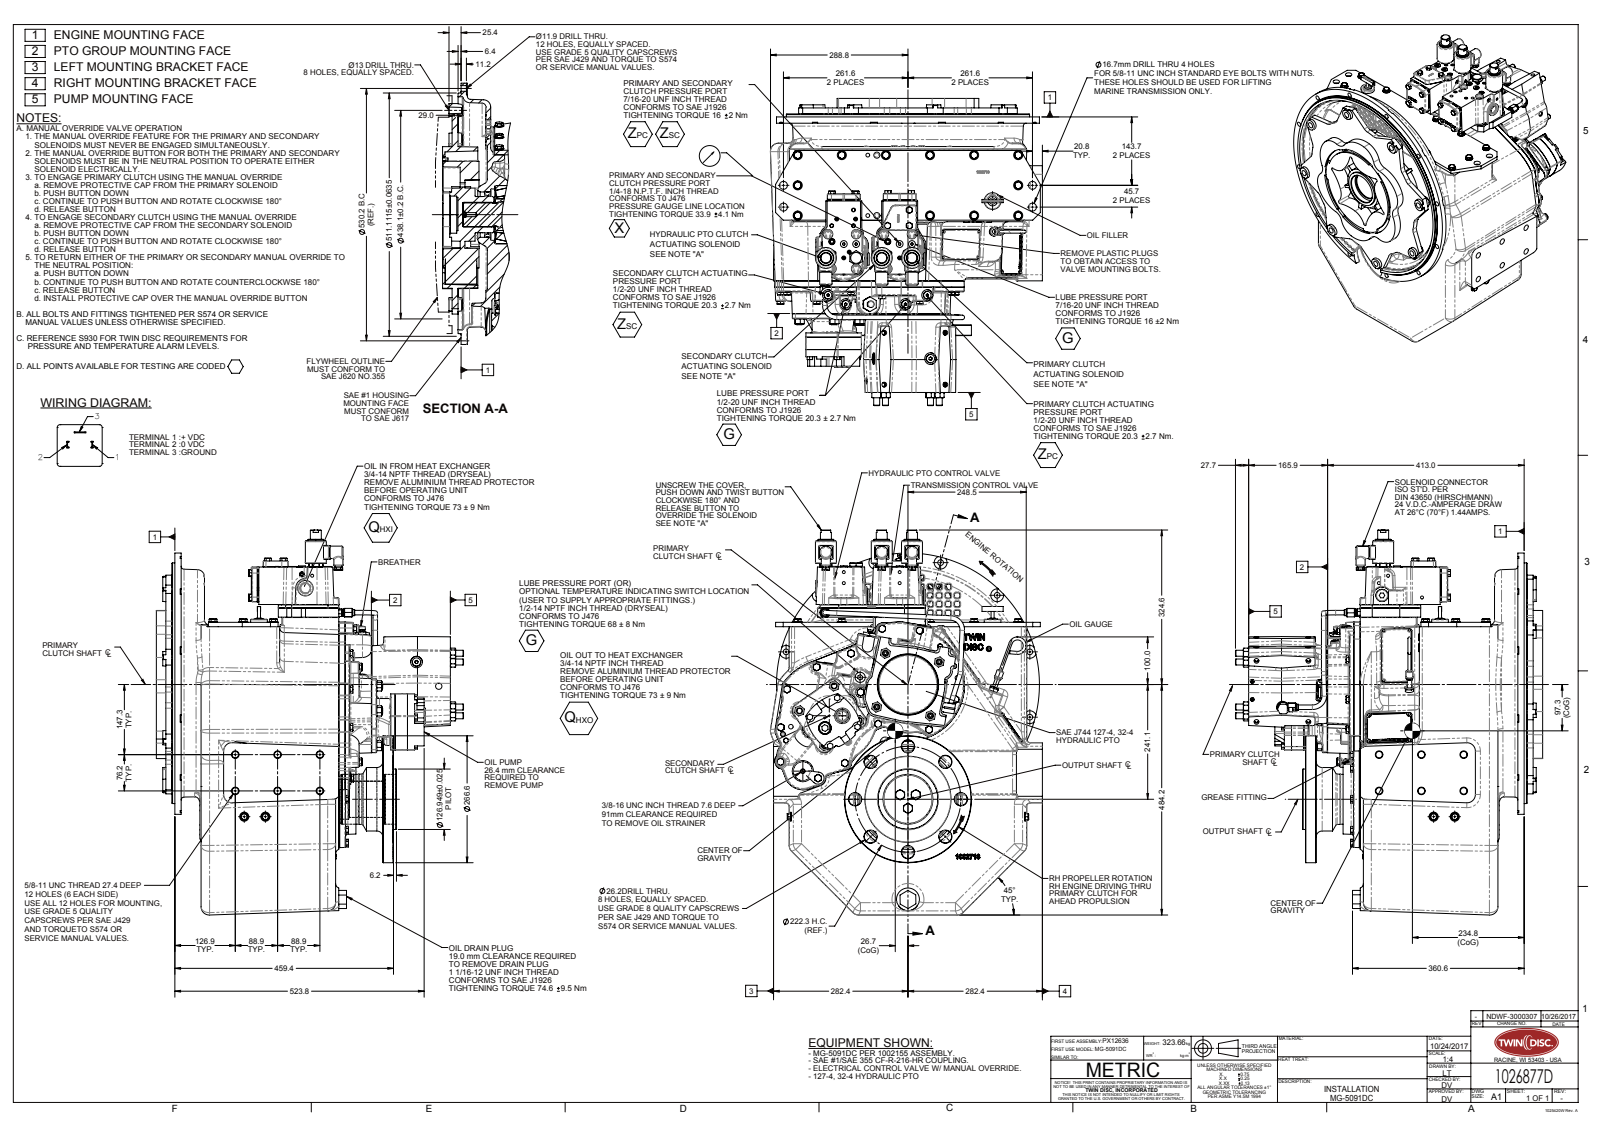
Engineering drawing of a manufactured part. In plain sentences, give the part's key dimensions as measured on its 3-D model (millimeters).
The part is named "1026877D". Its 3-D file was written by "SolidWorks 2015 (AUTOMOTIVE_DESIGN)". It is 0 solids with 3793 faces: 1477 planar, 972 cylindrical and 1344 other. Overall it measures 808.82 by 645.43 by 571.49 millimeters. Round holes: 12 of diameter 11.91, 8 of diameter 10, 8 of diameter 26.19, 8 of diameter 26.92, 6 of diameter 6.2, 6 of diameter 15.87, 5 of diameter 7.94, 4 of diameter 9.52, 4 of diameter 9.53, 4 of diameter 16.67, 3 of diameter 24.61, 2 of diameter 3. Round bosses or shafts: 14 of diameter 19.05, 13 of diameter 14.14, 8 of diameter 24, 8 of diameter 19.81, 7 of diameter 12.54, 6 of diameter 14.29, 5 of diameter 9.53, 4 of diameter 15.87. Partial cylindrical surfaces (rounded edges, fillets, slot ends): 118 of radius 3.05, 68 of radius 1.52, 30 of radius 2.03, 24 of radius 8.13, 24 of radius 10.16, 22 of radius 3, 21 of radius 2, 21 of radius 2.54. The main face-to-face distances are 0.42, 302.84, 302.42, 13.12, 13.54, 289.3, 9.27, 20.14, 19.72, 6.6. The hole center spacings are 459.18, 137.23, 265.1, 265.11, 374.92, 512.14, 88.9, 109.
